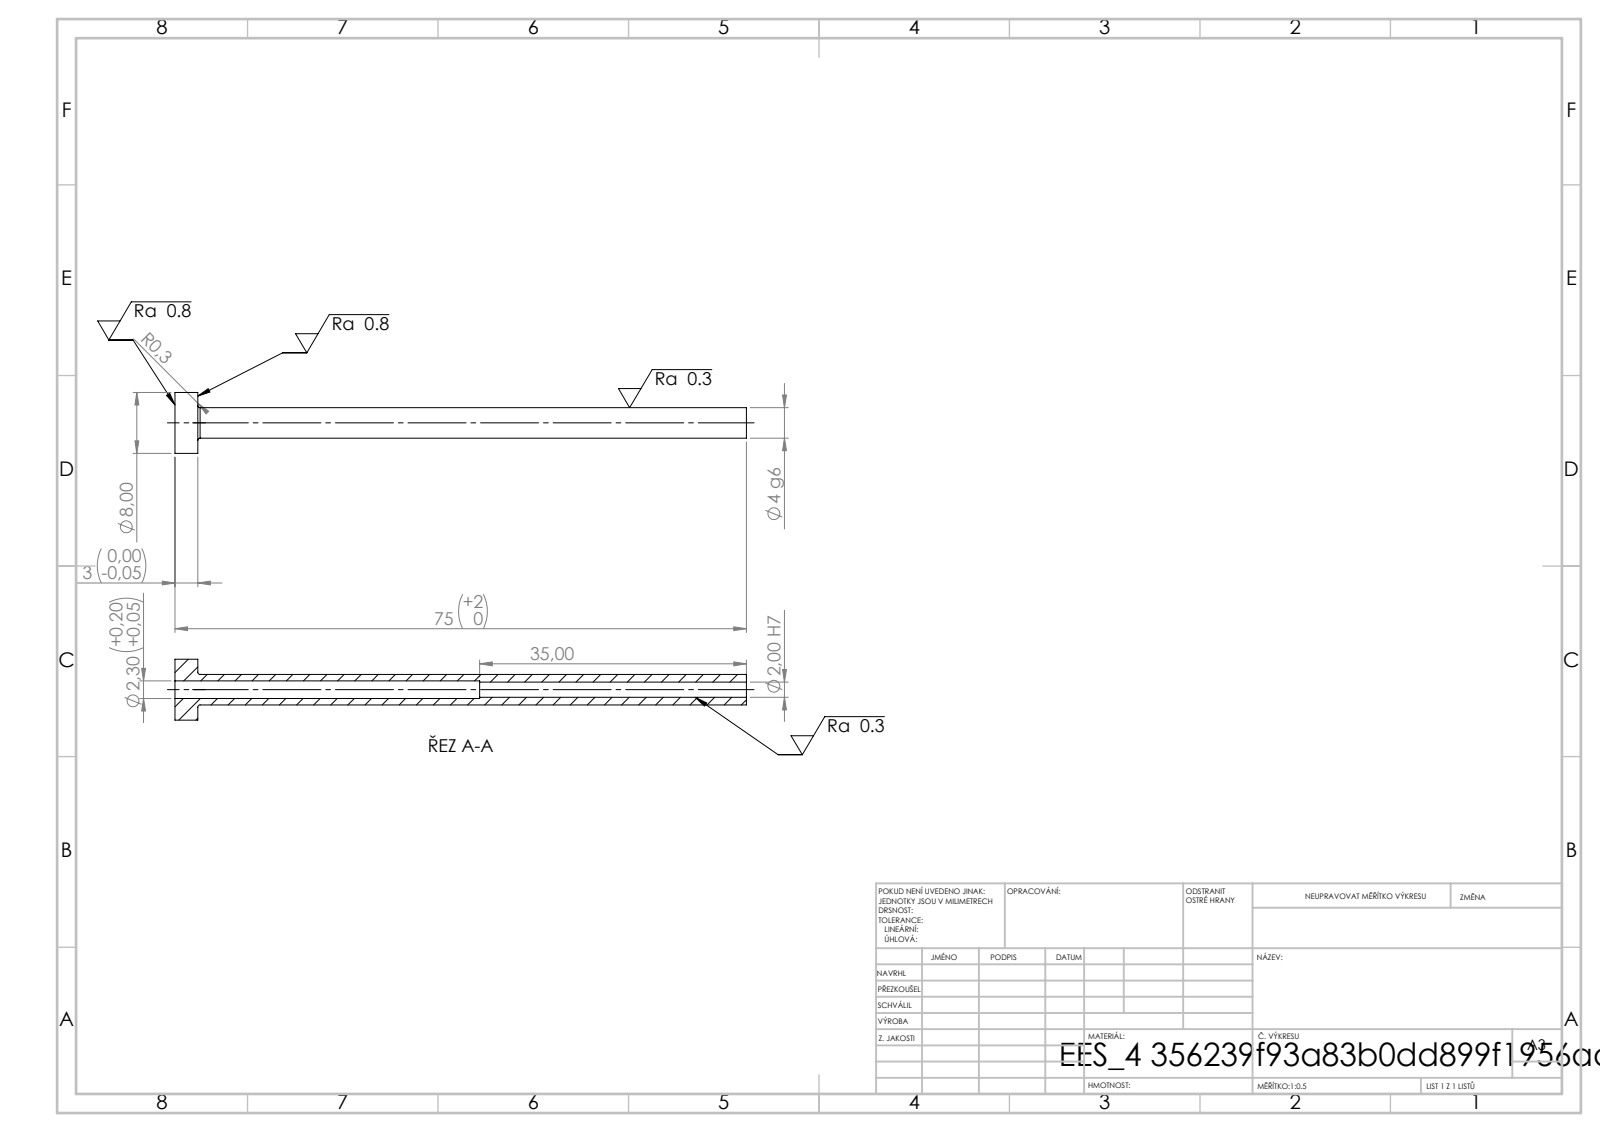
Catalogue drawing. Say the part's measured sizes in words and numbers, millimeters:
Its 3-D file was written by "SolidWorks 2019 (CONFIG_CONTROL_DESIGN)". It is 1 solid with 14 faces: 4 planar, 8 cylindrical and 2 other. Overall it measures 75 by 8 by 8 millimeters. Its volume is 780 cubic millimeters and its surface area 1 582 square millimeters. Round holes: 1 of diameter 2, 1 of diameter 2.3. Round bosses or shafts: 1 of diameter 8, 1 of diameter 4. The main face-to-face distances are 3, 75, 72, 40, 37, 35.
